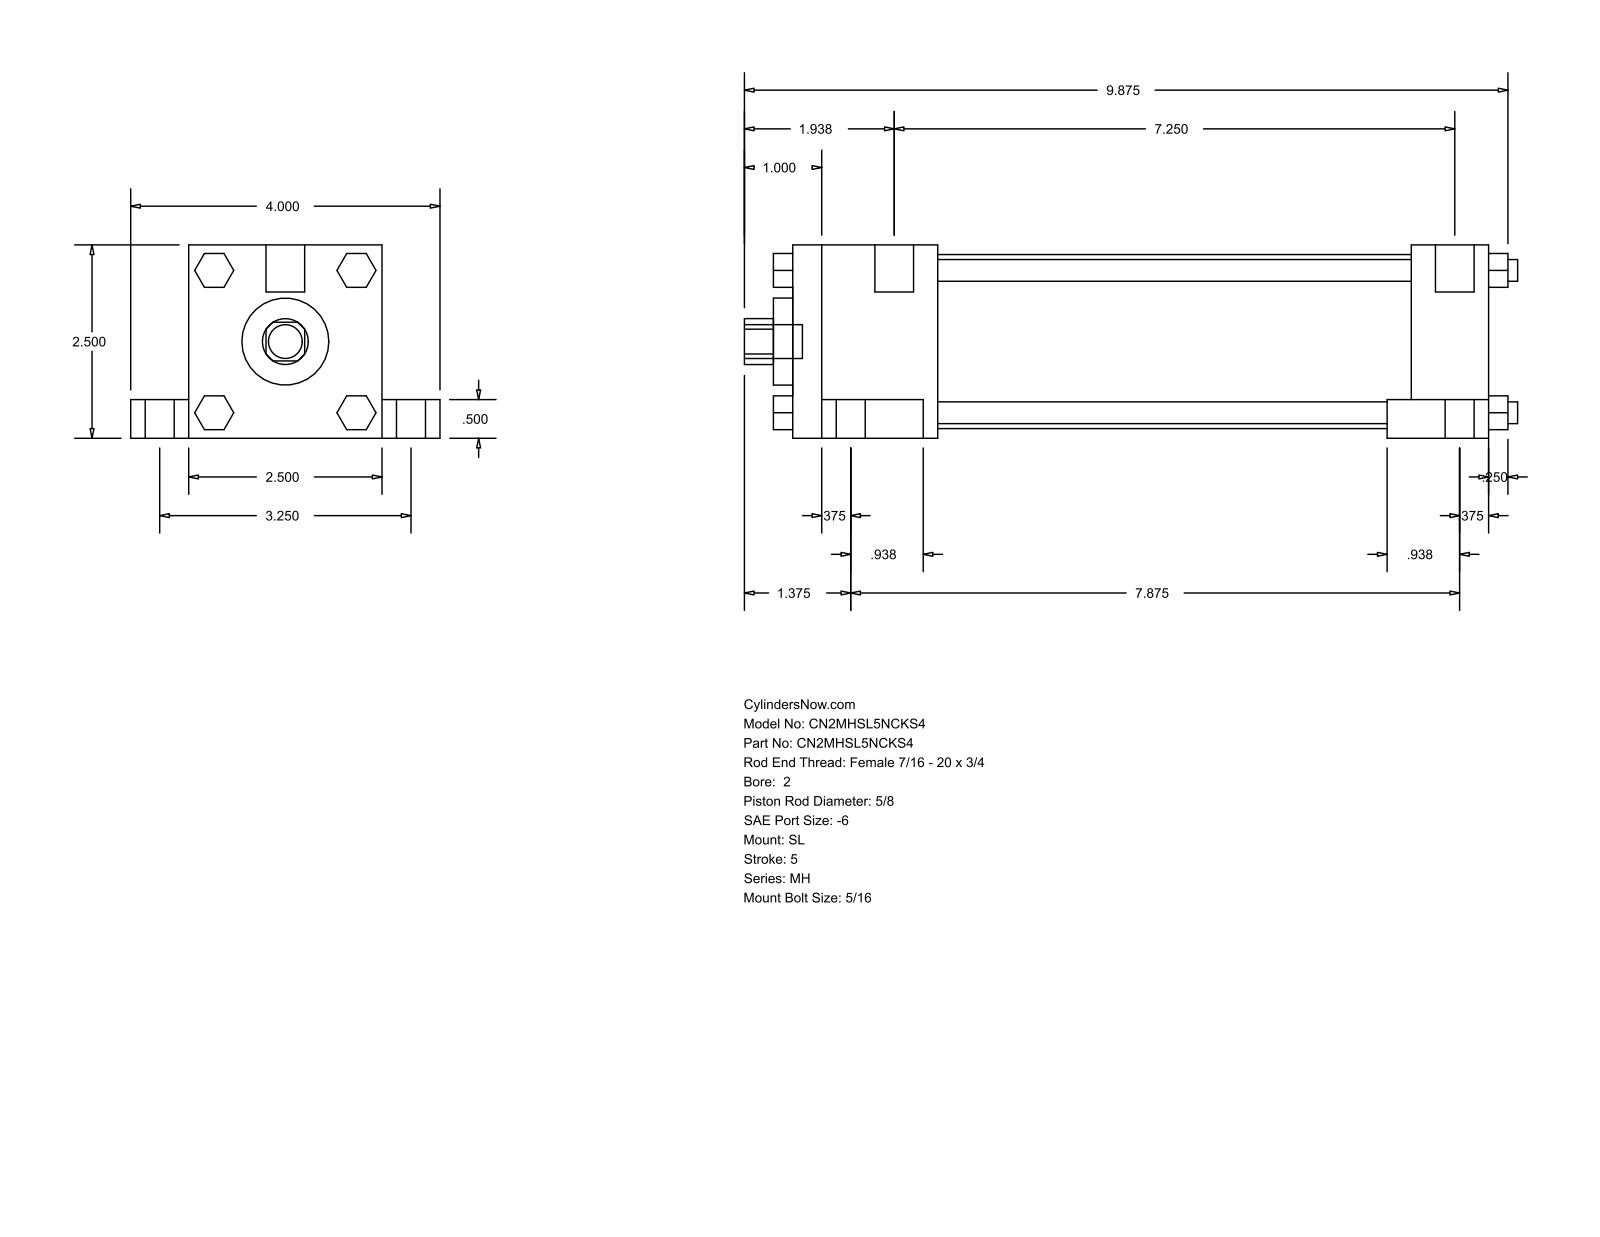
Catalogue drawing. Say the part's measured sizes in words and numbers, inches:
The part is named "MH_SL__0200_0.625". Its 3-D file was written by "GSSL Pune (CONFIG_CONTROL_DESIGN)". It is 0 solids with 148 faces: 112 planar, 36 cylindrical and 0 other. Overall it measures 10 by 4 by 2.5 inches. Round holes: 1 of diameter 0.625, 1 of diameter 1.125, 1 of diameter 2.25. Round bosses or shafts: 4 of diameter 0.625, 4 of diameter 0.375, 4 of diameter 0.281, 4 of diameter 0.219, 2 of diameter 0.5, 1 of diameter 0.437. Partial cylindrical surfaces (rounded edges, fillets, slot ends): 1 of radius 0.297. The main face-to-face distances are 2.5, 9, 0.5, 0.75, 2, 3.25, 1, 8, 1.875, 6.125.
